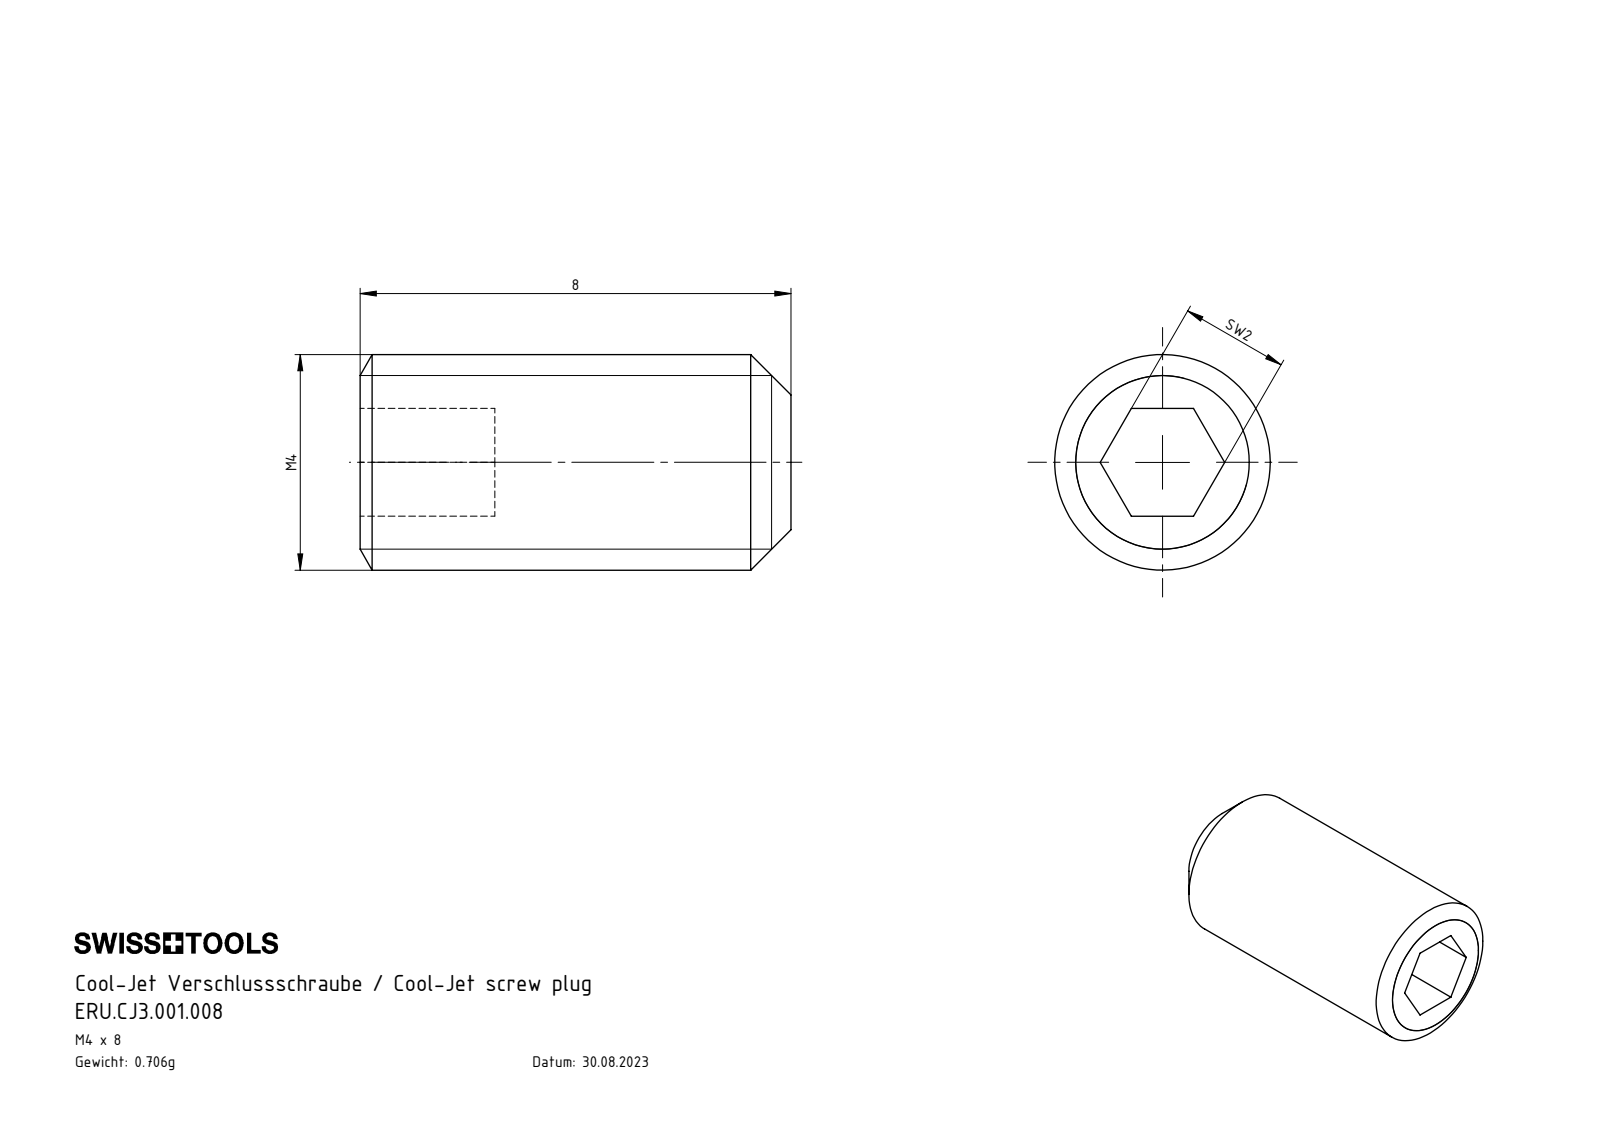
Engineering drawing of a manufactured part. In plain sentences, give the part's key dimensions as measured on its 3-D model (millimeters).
The part is named "ERU.CJ3.001.008". Its 3-D file was written by "SolidWorks 2017 (AUTOMOTIVE_DESIGN)". It is 1 solid with 15 faces: 9 planar, 2 cylindrical and 4 other. Overall it measures 8 by 4 by 4 millimeters. Its volume is 88 cubic millimeters and its surface area 135 square millimeters. Round bosses or shafts: 1 of diameter 4. The main face-to-face distances are 2, 8, 2.5, 5.5.
